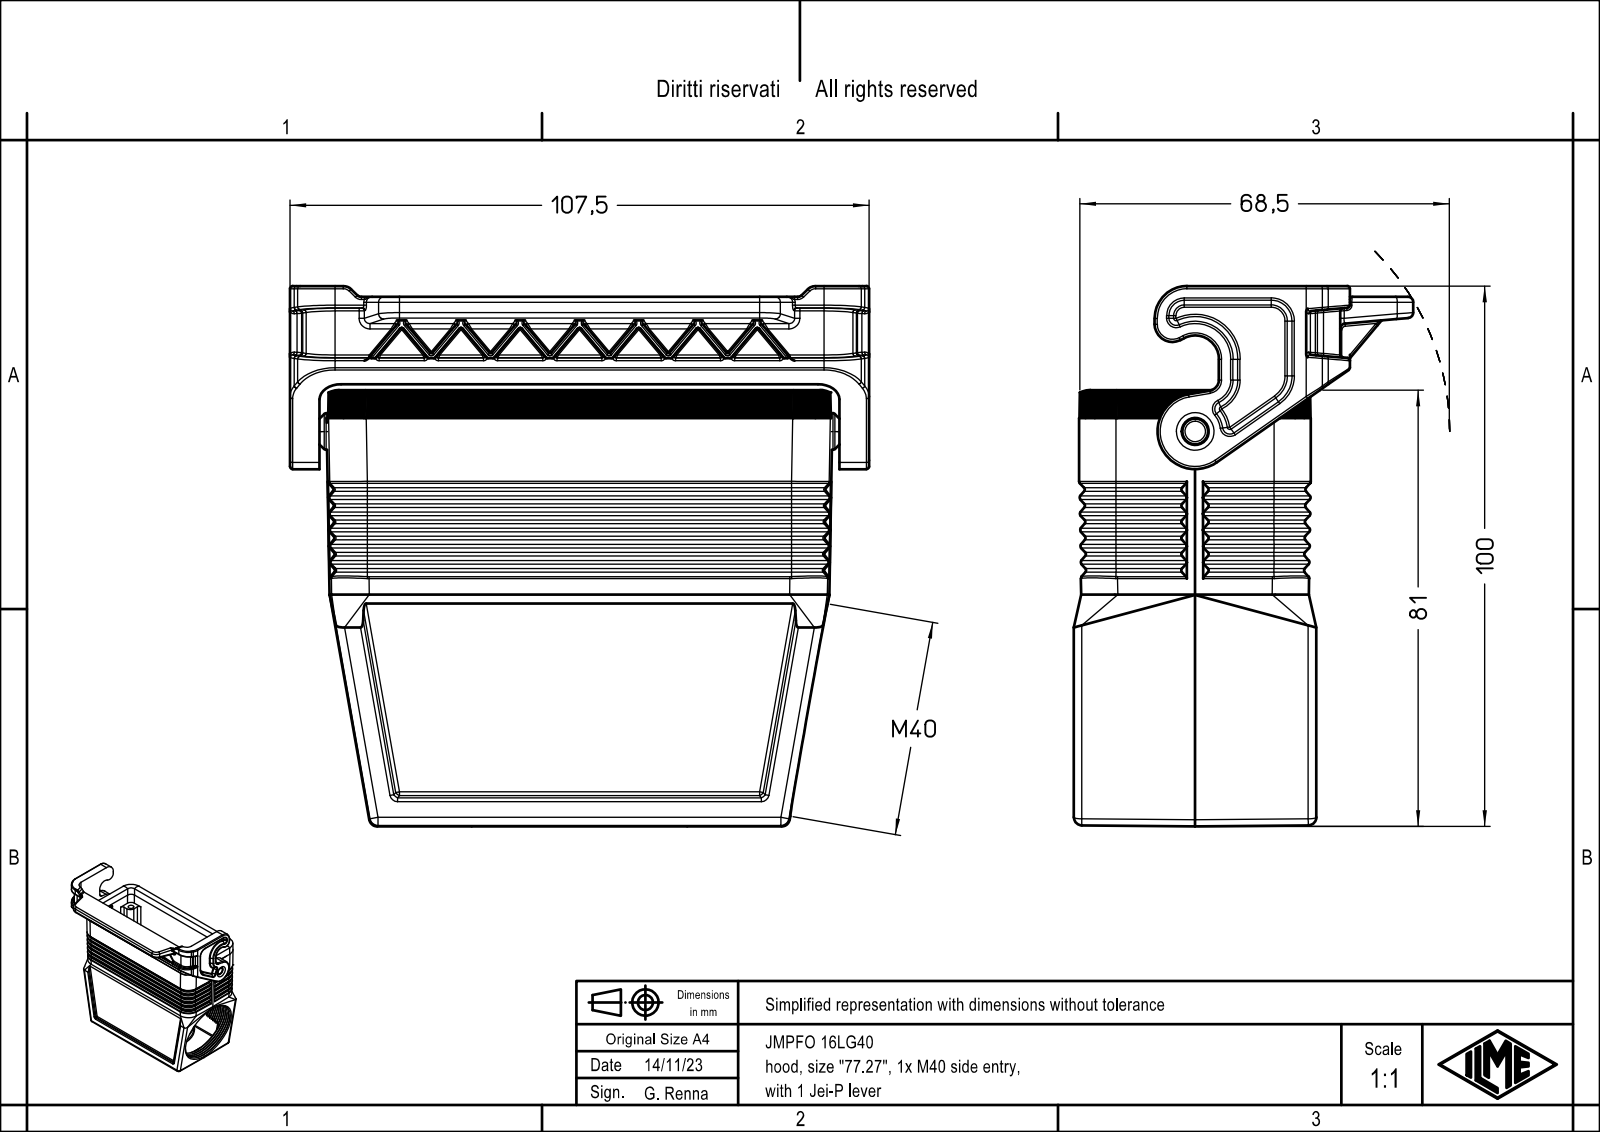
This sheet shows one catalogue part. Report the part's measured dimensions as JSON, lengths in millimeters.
{"part_name": "JMPFO 16LG40", "step_written_by": "Creo Elements/Direct Modeling 20.1B 02-Apr-2019 (C) Parametric Technology GmbH (AUTOMOTIVE_DESIGN)", "units": "millimeters", "bodies": {"solids": 1, "faces": 1192, "planar": 347, "cylindrical": 435, "other": 410}, "overall_size": [107.5, 100.25, 63], "volume_mm3": 105869, "surface_area_mm2": 56467, "round_holes": [[3, 4], [3.5, 4], [4.8, 1], [38.6, 1]], "round_bosses_or_shafts": [[6.8, 1]], "partial_cylinders_radius": [[0.5, 147], [0.3, 99], [1, 27], [1.5, 22], [0.33, 15], [7, 13], [3, 12], [4, 8]], "face_to_face_distances": [3.75, 39.25, 35.5, 43, 2, 7, 4, 3.25, 42.5, 46.25], "hole_center_spacings": [27, 77.5, 82.07]}
